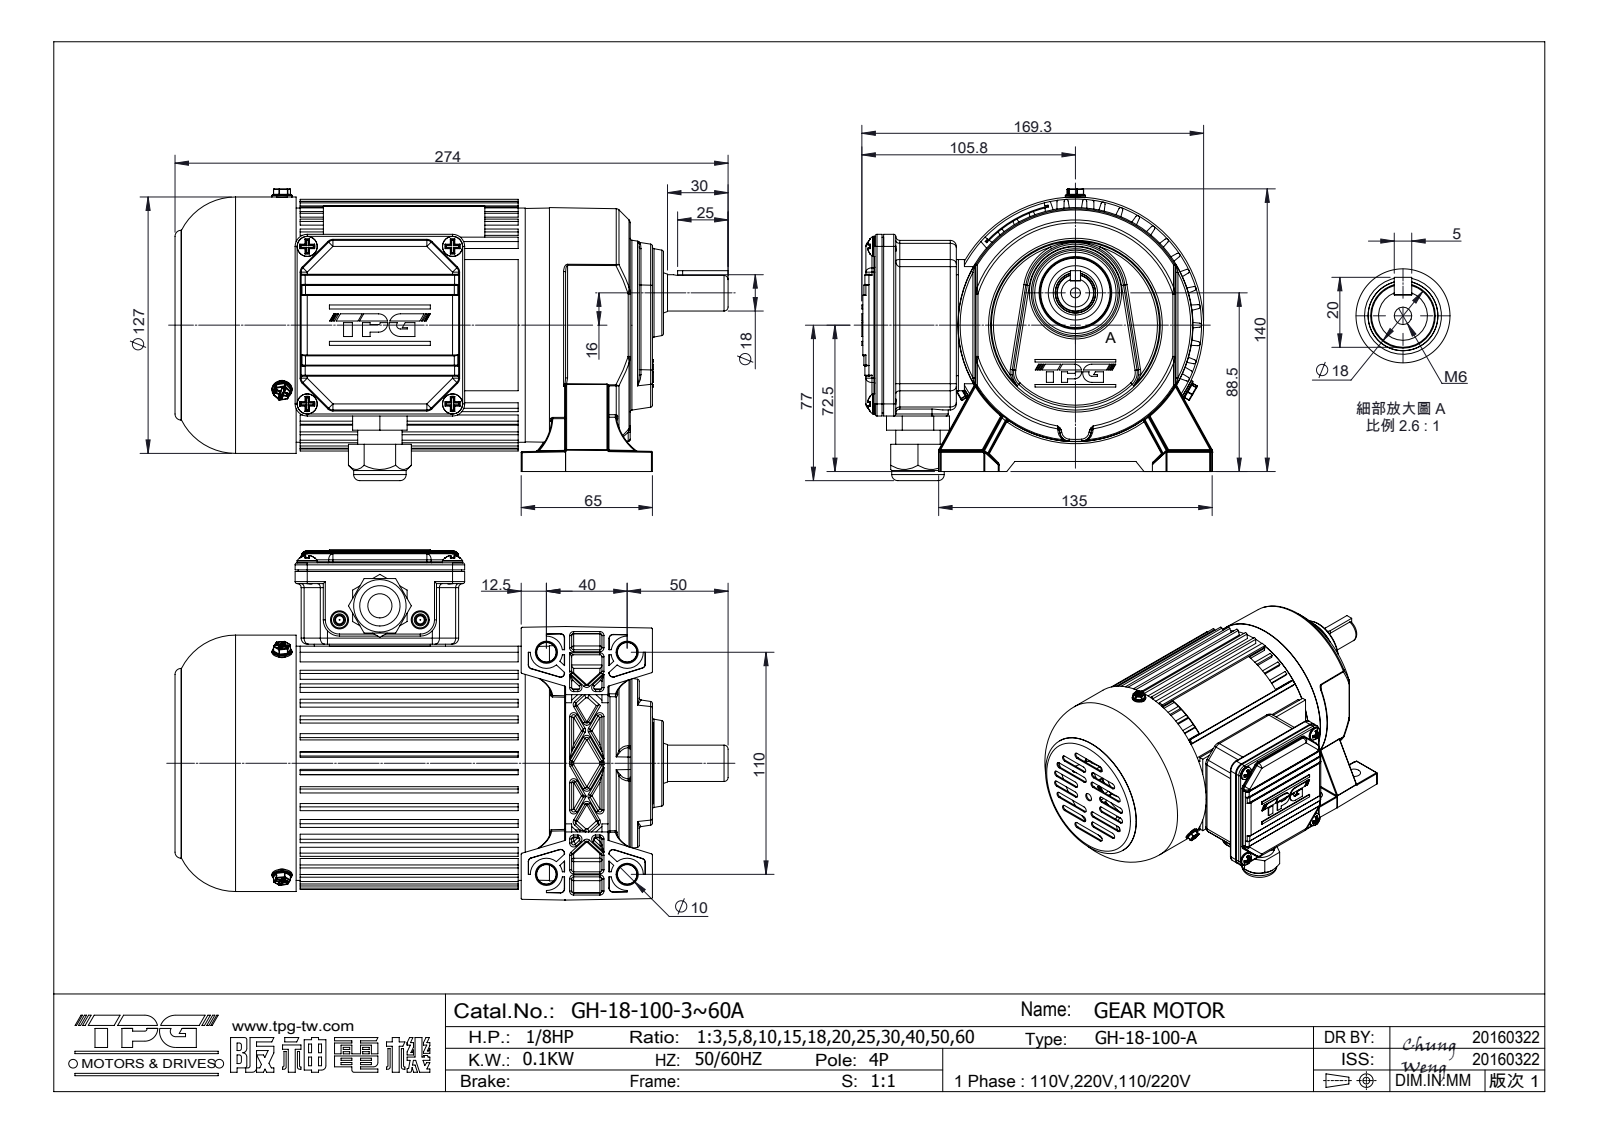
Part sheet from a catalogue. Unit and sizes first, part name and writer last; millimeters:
Units: millimetres
Overall size (bounding box): 274 × 173.56 × 144.5
Round holes (diameter × count): ⌀4.2 ×16, ⌀6 ×13, ⌀3 ×8, ⌀5 ×6, ⌀4 ×5, ⌀12 ×3, ⌀8 ×2, ⌀9 ×2, ⌀19 ×2, ⌀20 ×2, ⌀35 ×2, ⌀10 ×1
Round bosses / shafts (diameter × count): ⌀10 ×11, ⌀5 ×7, ⌀22 ×3, ⌀26 ×2, ⌀127 ×1, ⌀125 ×1, ⌀116 ×1, ⌀110 ×1
Partial cylindrical surfaces — rounded edges, fillets, slot ends (radius × count): R0.3 ×396, R1 ×183, R0.5 ×175, R0.2 ×130, R2 ×49, R1.5 ×40, R2.25 ×28, R3 ×26
Main face-to-face distances: 4, 1.5, 3, 37, 7, 2.5, 3.5, 1, 8, 11
Hole centre spacings: 6.5, 44.07, 47.27, 50, 52.84, 68.5, 86, 12.02
Volume: 576 886 mm³ · Surface area: 457 087 mm²
Bodies: 26 solids, 5258 faces (1299 planar, 1710 cylindrical, 2249 other)
Part name (STEP PRODUCT): GH-18-100-A
STEP written by: SolidWorks 2012 (CONFIG_CONTROL_DESIGN)
